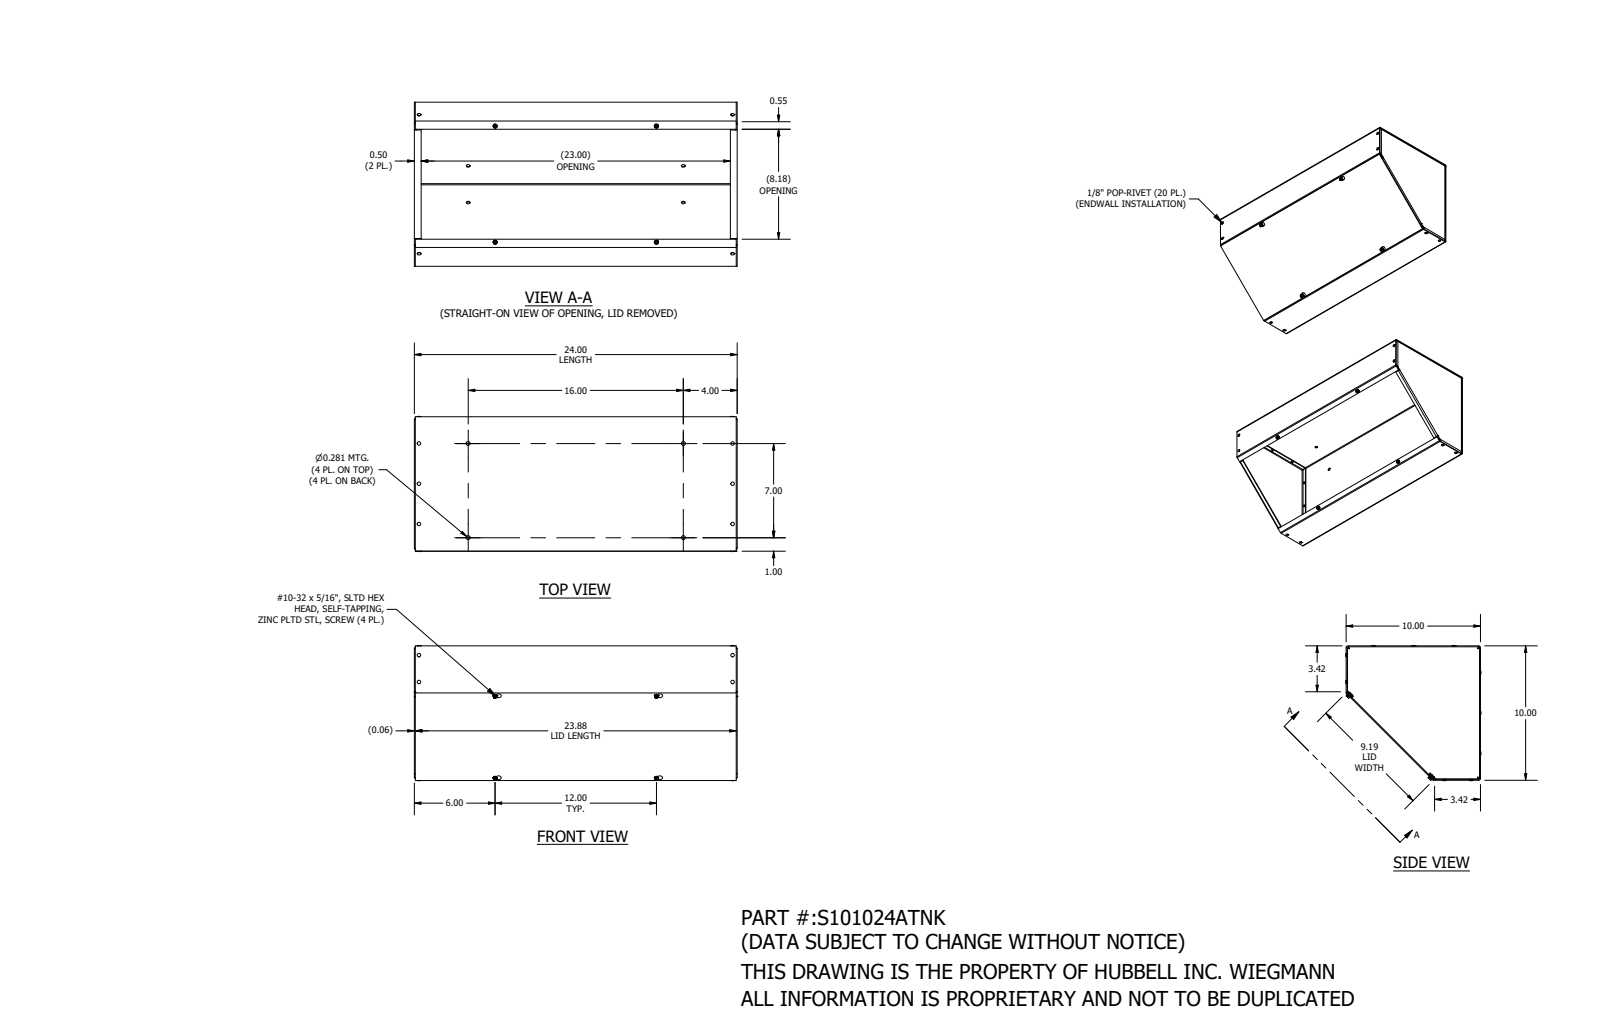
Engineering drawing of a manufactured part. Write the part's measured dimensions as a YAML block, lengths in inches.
part_name: "S101024ATNK"
step_written_by: "SolidWorks 2021 (AUTOMOTIVE_DESIGN)"
units: inches
bodies: {solids: 28, faces: 1128, planar: 288, cylindrical: 344, other: 496}
overall_size: [24, 10.08, 10.08]
volume: 78.08
surface_area: 2134
round_holes:
  - {diameter: 0.129, count: 20}
  - {diameter: 0.281, count: 8}
  - {diameter: 0.171, count: 4}
  - {diameter: 0.406, count: 4}
round_bosses_or_shafts:
  - {diameter: 0.262, count: 20}
  - {diameter: 0.125, count: 19}
  - {diameter: 0.313, count: 4}
  - {diameter: 0.181, count: 4}
  - {diameter: 0.125, count: 1}
partial_cylinders:
  - {radius: 0.064, count: 40}
  - {radius: 0.136, count: 15}
  - {radius: 0.063, count: 11}
  - {radius: 0.062, count: 4}
  - {radius: 0.109, count: 4}
face_to_face_distances: [0.074, 9.926, 9.852, 10, 23.926, 24, 23.852, 0.068, 0.142, 0.148]
hole_center_spacings: [23.313, 3, 23.505, 0.25, 0.71, 1.29, 2, 2.29]
